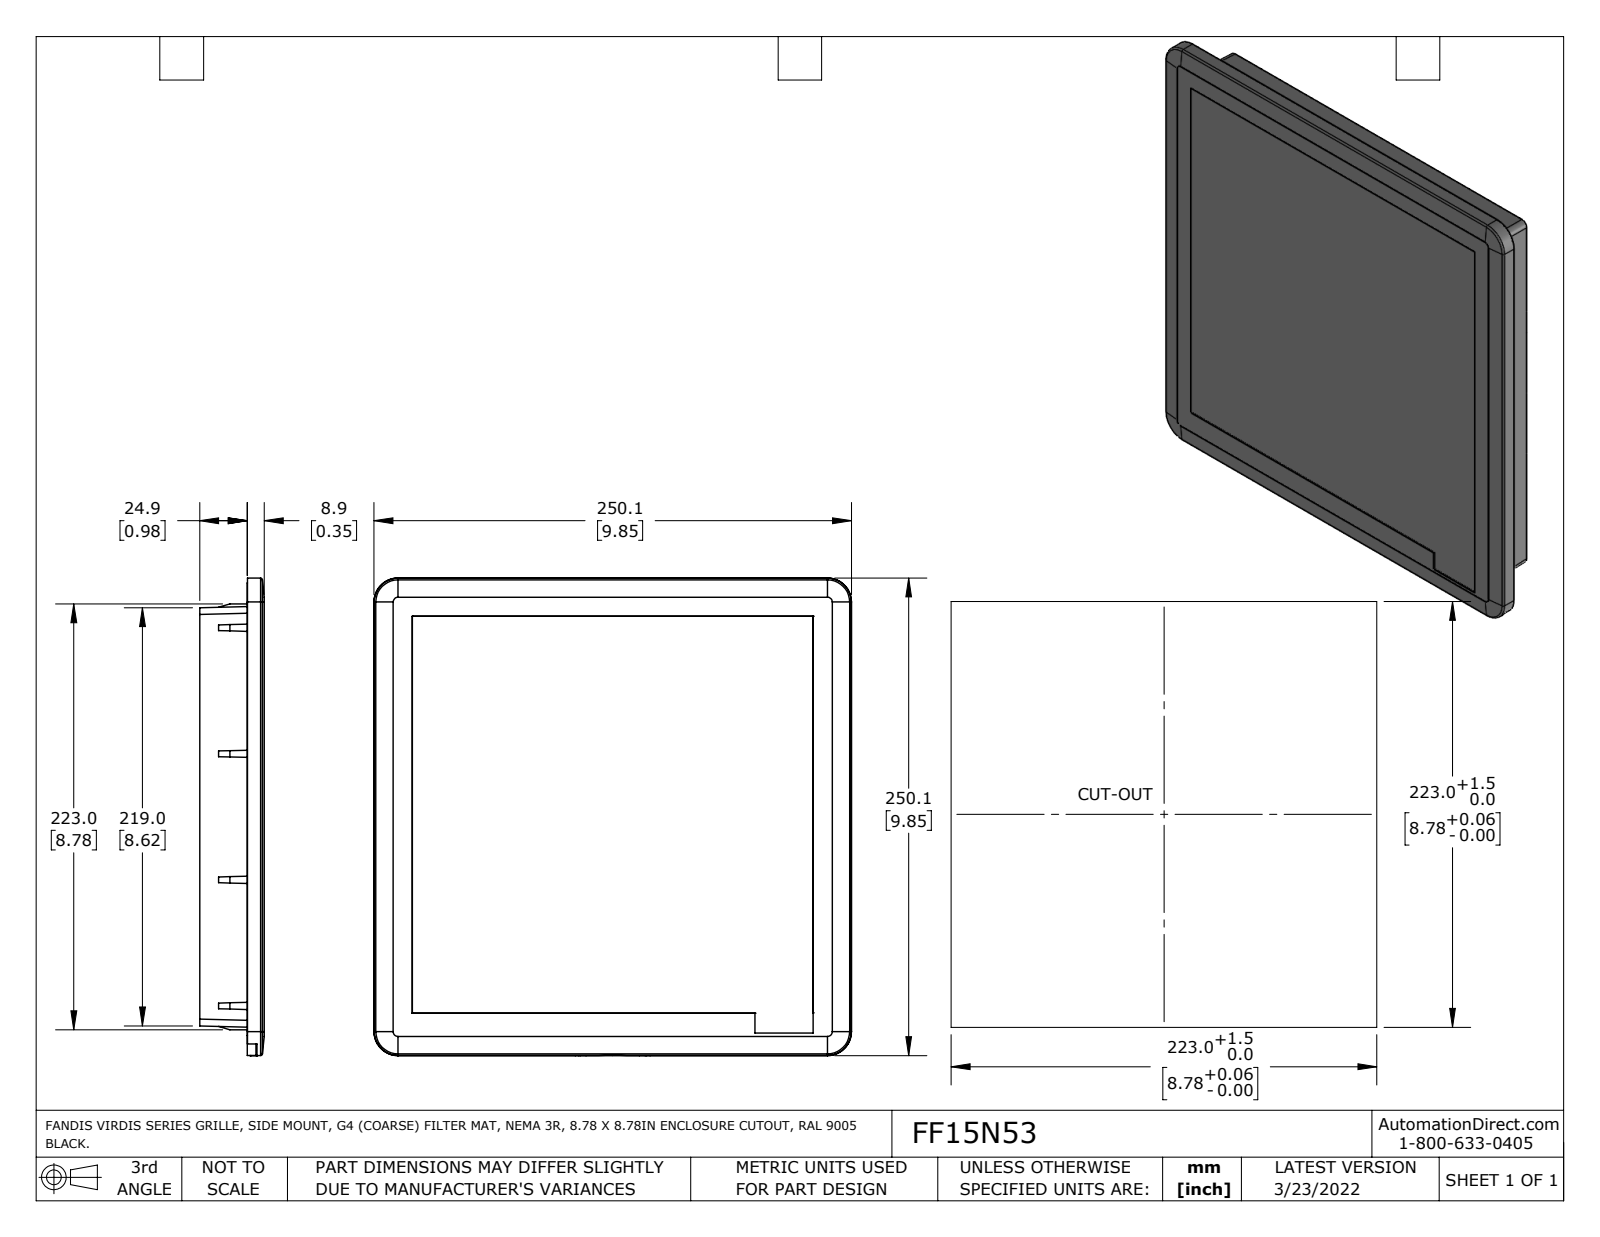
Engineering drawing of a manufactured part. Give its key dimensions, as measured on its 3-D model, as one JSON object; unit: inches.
{"part_name": "FF15y (p.c.)_REV1", "step_written_by": "SolidWorks 2021 (AUTOMOTIVE_DESIGN)", "units": "inches", "bodies": {"solids": 1, "faces": 276, "planar": 220, "cylindrical": 40, "other": 16}, "overall_size": [9.847, 9.847, 1.331], "volume_in3": 105.1, "surface_area_in2": 256, "partial_cylinders_radius": [[0.051, 8], [0.039, 4], [0.257, 4], [0.413, 4], [0.421, 4], [0.14, 2], [0.14, 2]], "face_to_face_distances": [1.311, 0.331, 0.98, 0.02, 0.35, 1.331, 0.028, 9.673, 0.346, 0.327]}
